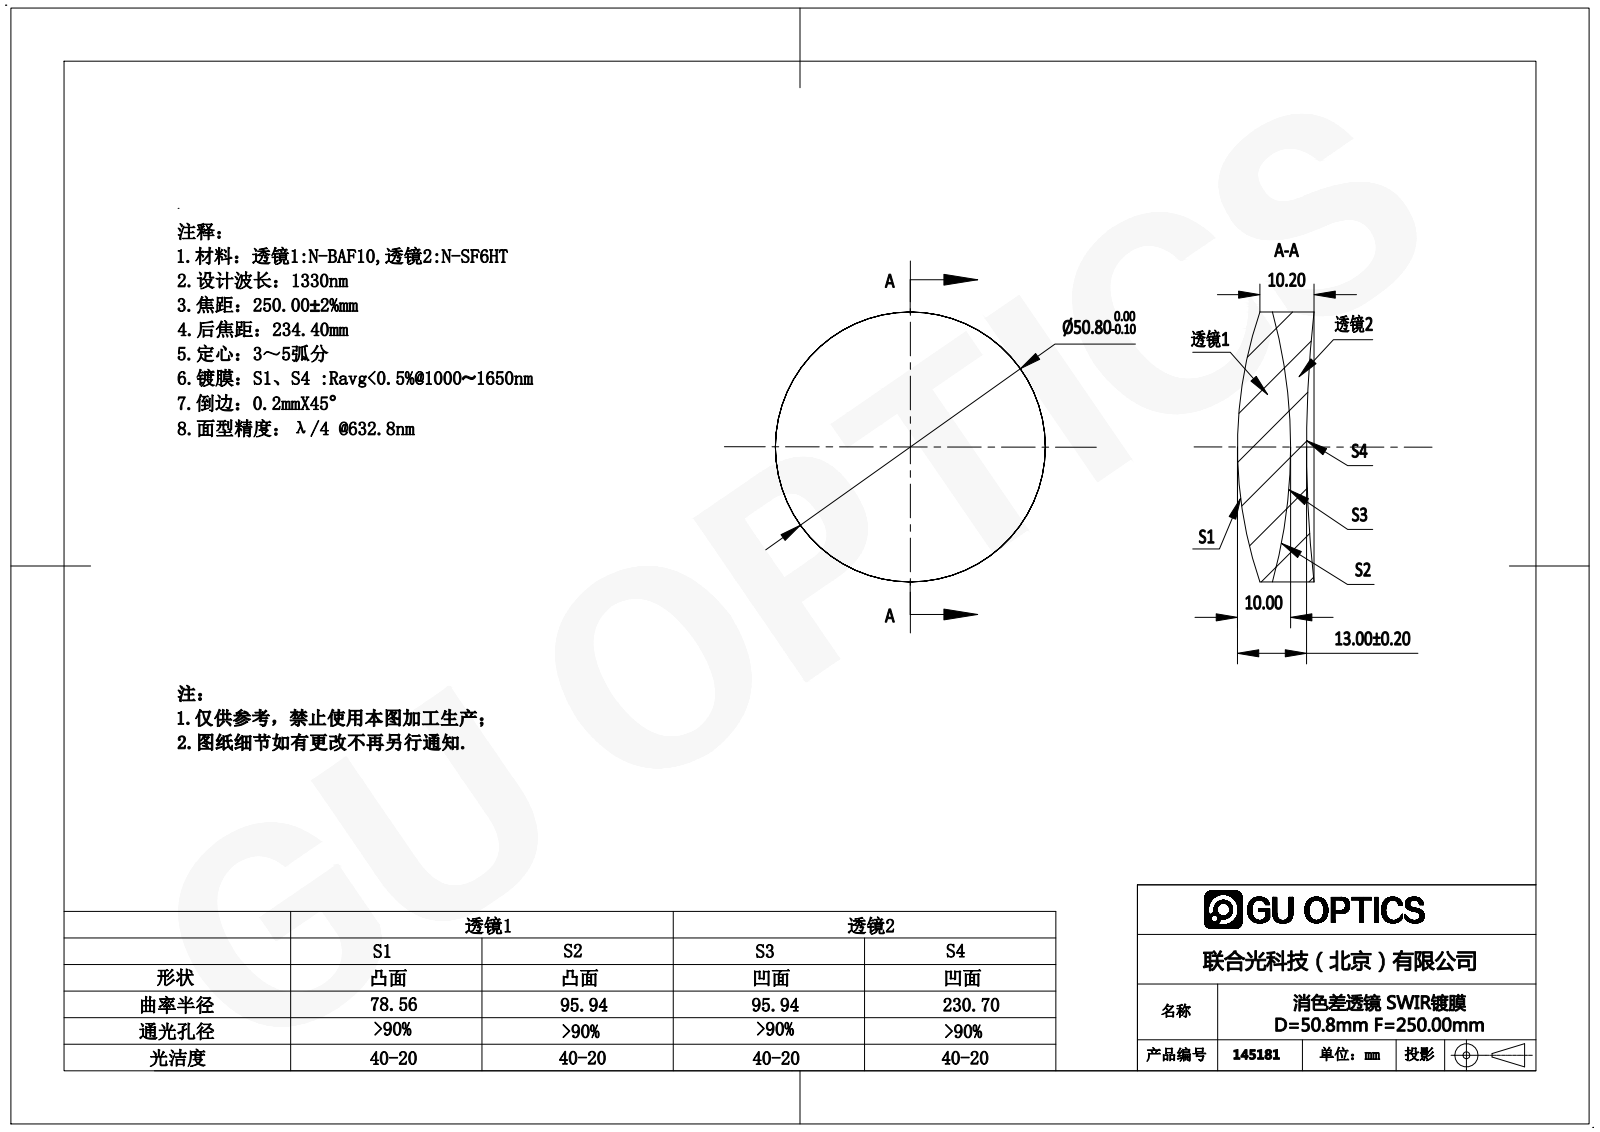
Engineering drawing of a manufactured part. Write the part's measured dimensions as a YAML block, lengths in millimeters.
part_name: "145181"
step_written_by: "SolidWorks 2016 (AUTOMOTIVE_DESIGN)"
units: millimeters
bodies: {solids: 2, faces: 12, planar: 0, cylindrical: 4, other: 8}
overall_size: [50.8, 50.8, 14.4]
volume: 23532
surface_area: 9868
round_bosses_or_shafts:
  - {diameter: 50.8, count: 1}
